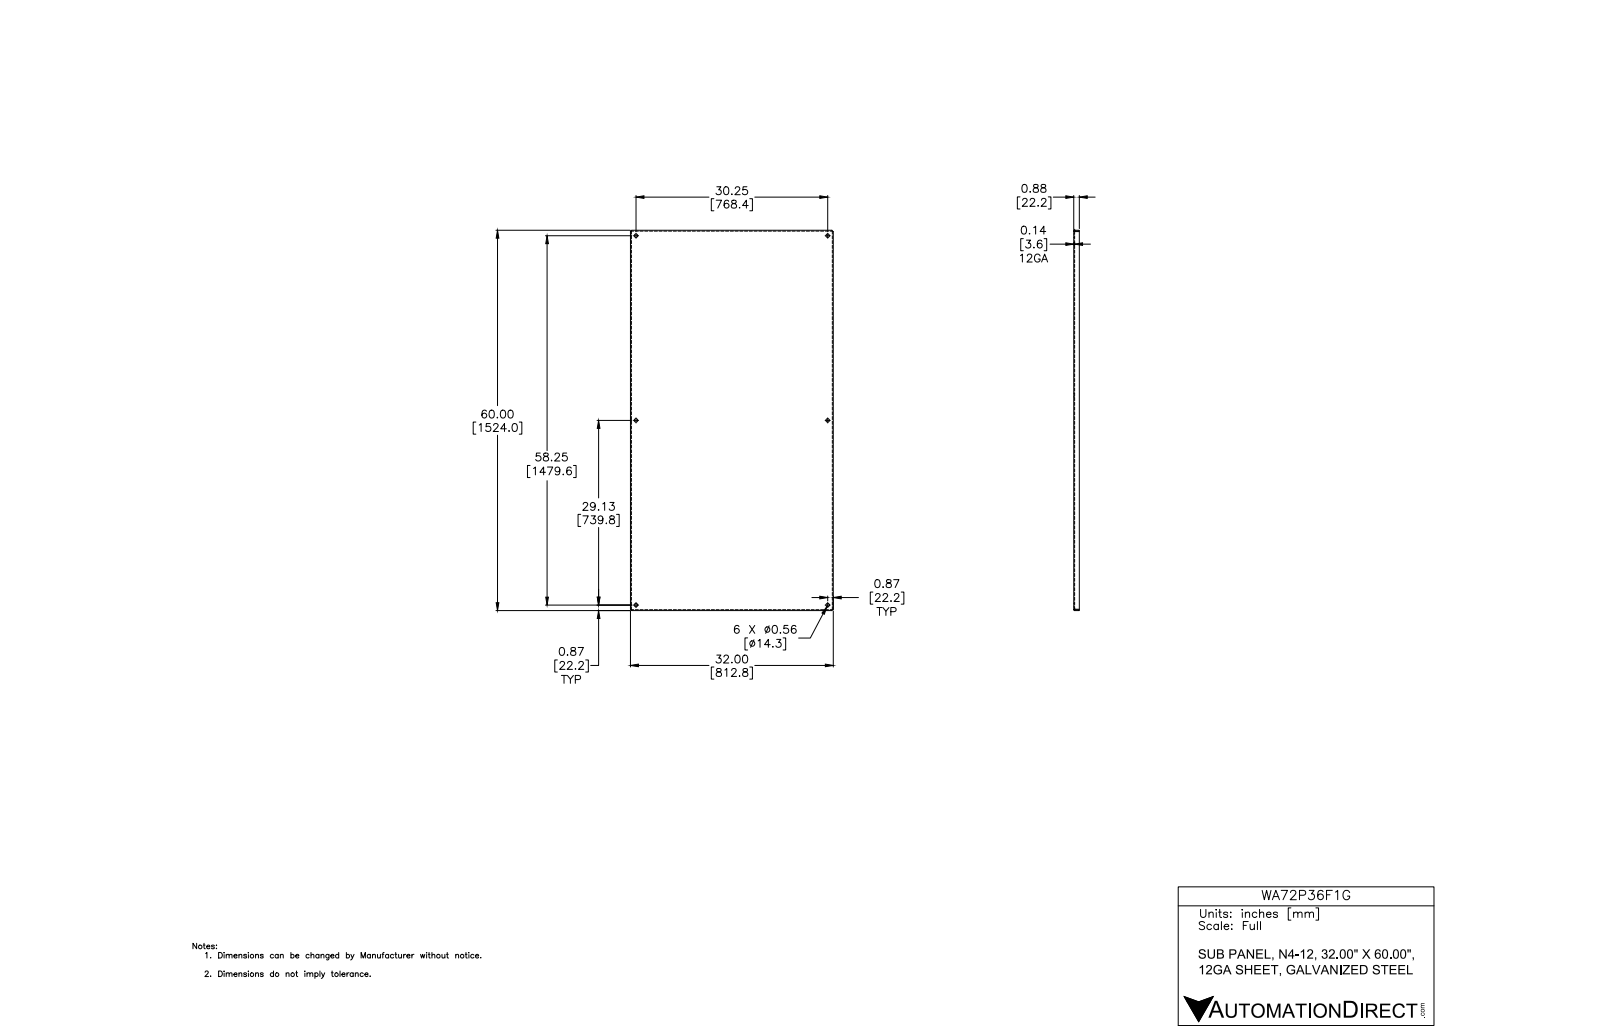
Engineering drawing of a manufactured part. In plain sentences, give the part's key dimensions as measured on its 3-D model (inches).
The part is named "WA_P_F_G". Its 3-D file was written by "Autodesk Inventor 2012 (AUTOMOTIVE_DESIGN)". It is 1 solid with 44 faces: 22 planar, 14 cylindrical and 8 other. Overall it measures 60 by 32 by 0.875 inches. Its volume is 192.8 cubic inches and its surface area 4 131 square inches. Round holes: 6 of diameter 0.563. Partial cylindrical surfaces (rounded edges, fillets, slot ends): 4 of radius 0.016, 4 of radius 0.109. The main face-to-face distances are 0.094, 31.906, 59.906, 32, 31.813, 60, 59.813, 0.781, 0.875, 0.16. The hole center spacings are 29.125, 29.125, 30.25, 41.992, 58.25, 65.636, 30.25, 41.992.
